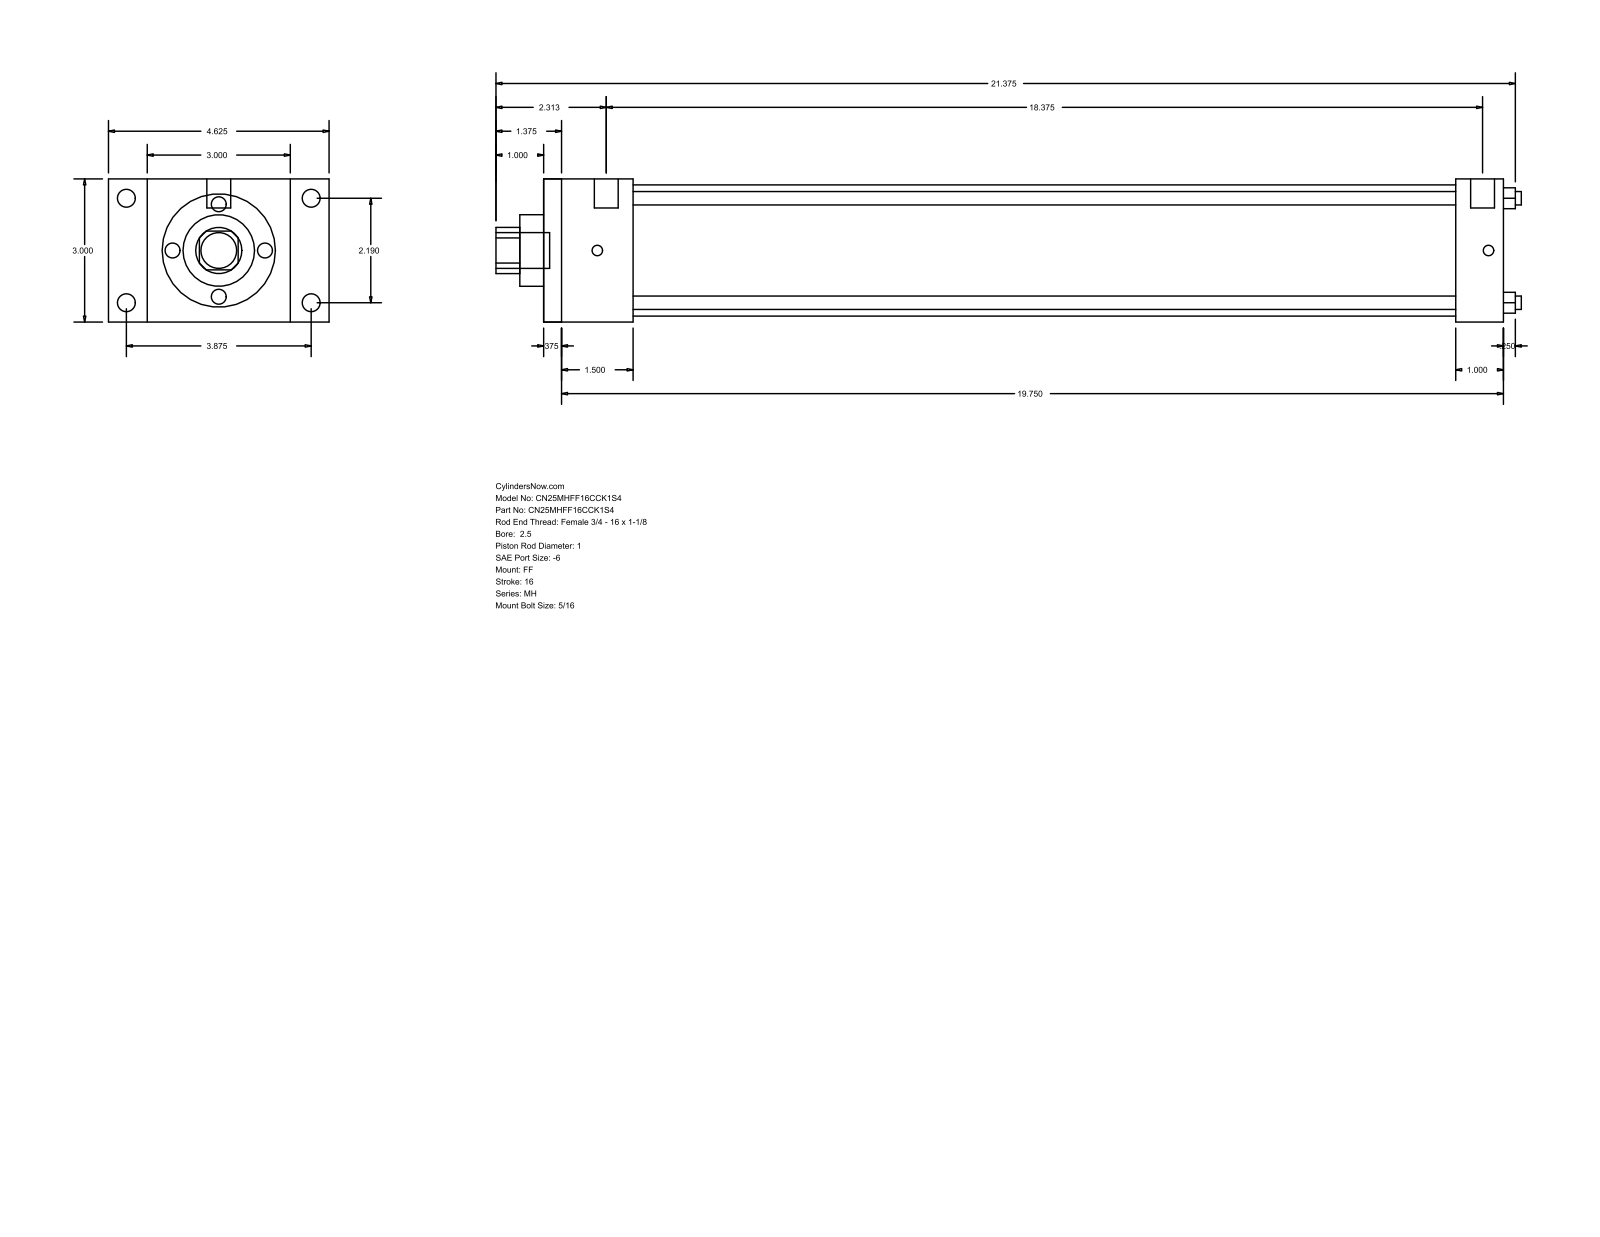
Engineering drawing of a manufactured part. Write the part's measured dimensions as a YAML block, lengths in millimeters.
part_name: "MH_FF__0250_1"
step_written_by: "GSSL Pune (CONFIG_CONTROL_DESIGN)"
units: millimeters
bodies: {solids: 0, faces: 92, planar: 64, cylindrical: 28, other: 0}
overall_size: [546.1, 117.47, 76.2]
round_holes:
  - {diameter: 7.14, count: 4}
  - {diameter: 25.4, count: 1}
  - {diameter: 38.1, count: 1}
  - {diameter: 69.85, count: 1}
round_bosses_or_shafts:
  - {diameter: 9.53, count: 4}
  - {diameter: 5.56, count: 4}
  - {diameter: 12.7, count: 2}
  - {diameter: 19.05, count: 1}
partial_cylinders:
  - {radius: 12.29, count: 1}
face_to_face_distances: [76.2, 511.18, 9.52, 501.66, 25.4, 47.63, 485.78, 38.11, 476.26, 438.15]
hole_center_spacings: [39.33, 55.62, 78.66]
